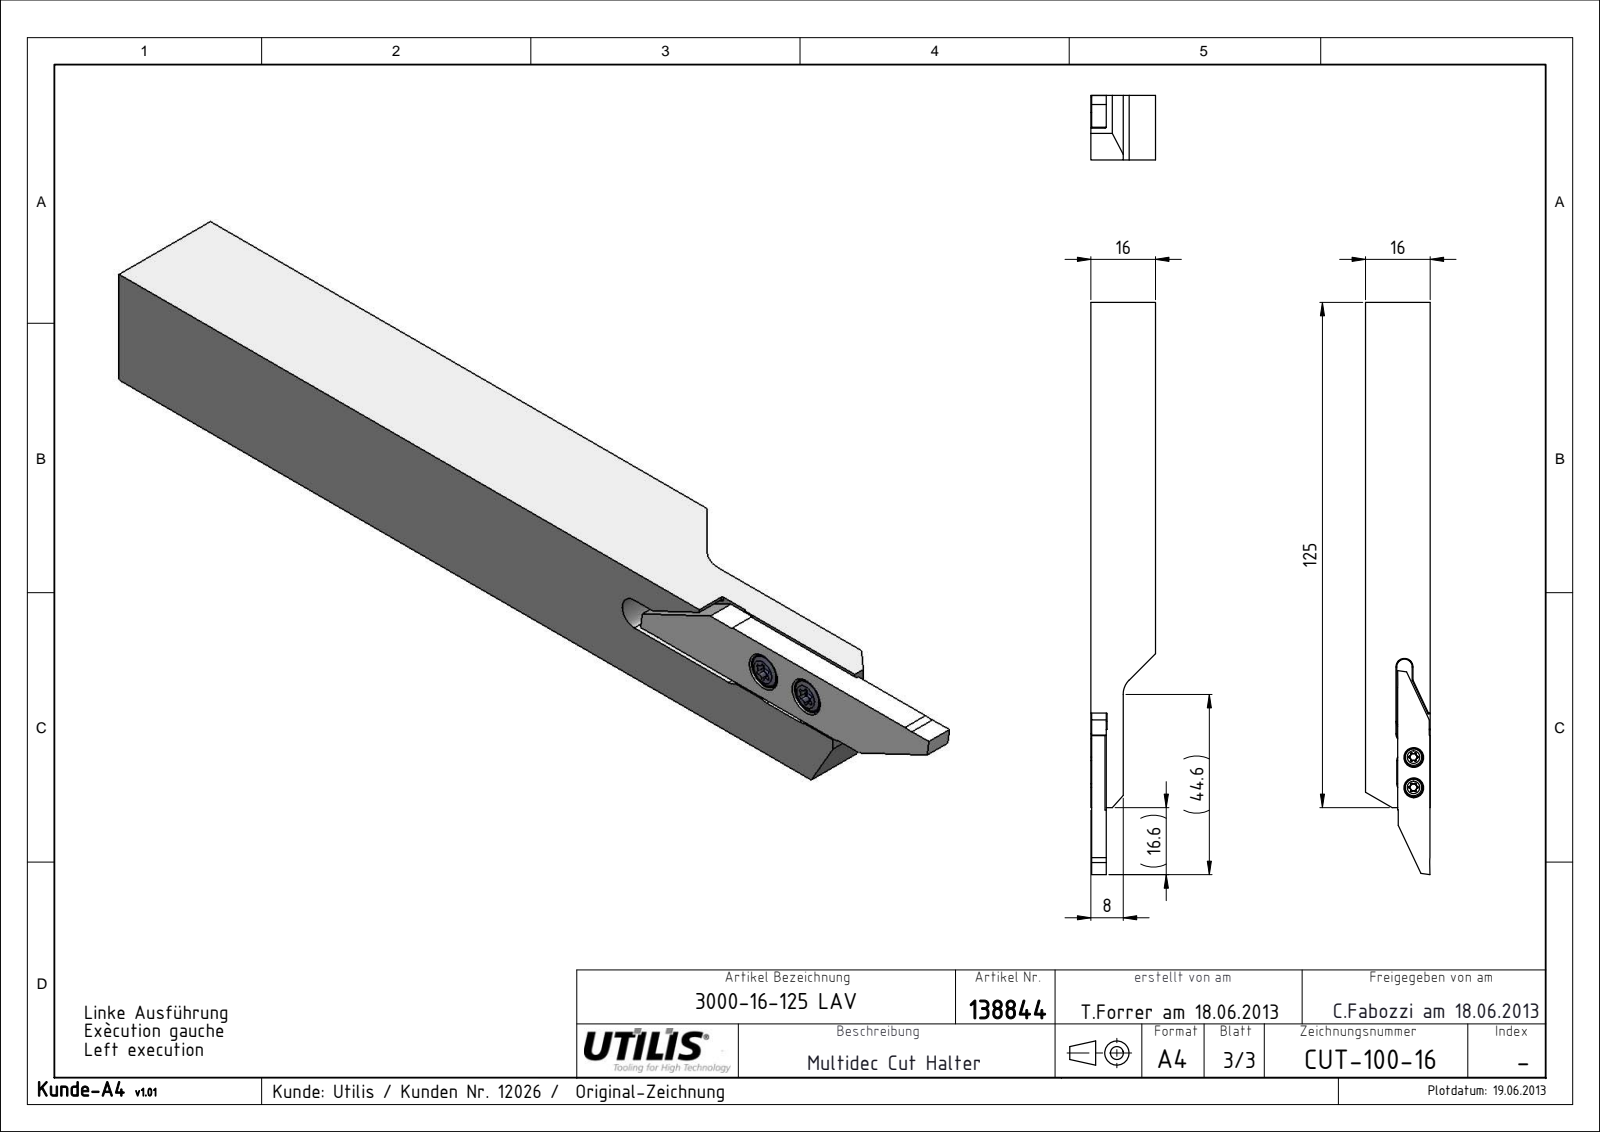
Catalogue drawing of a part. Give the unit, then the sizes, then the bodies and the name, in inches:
Units: inches
Overall size (bounding box): 5.575 × 0.63 × 0.63
Partial cylindrical surfaces — rounded edges, fillets, slot ends (radius × count): R0.083 ×4, R0.394 ×2, R0.197 ×1
Main face-to-face distances: 0.63, 0.315, 0.307, 0.622, 0.165, 0.15, 0.142, 0.48, 0.628, 0.313
Volume: 1.69 in³ · Surface area: 13.04 in²
Bodies: 1 solid, 45 faces (33 planar, 8 cylindrical, 4 other)
Part name (STEP PRODUCT): CUT-100-16
STEP written by: SolidWorks 2016 (AUTOMOTIVE_DESIGN)
